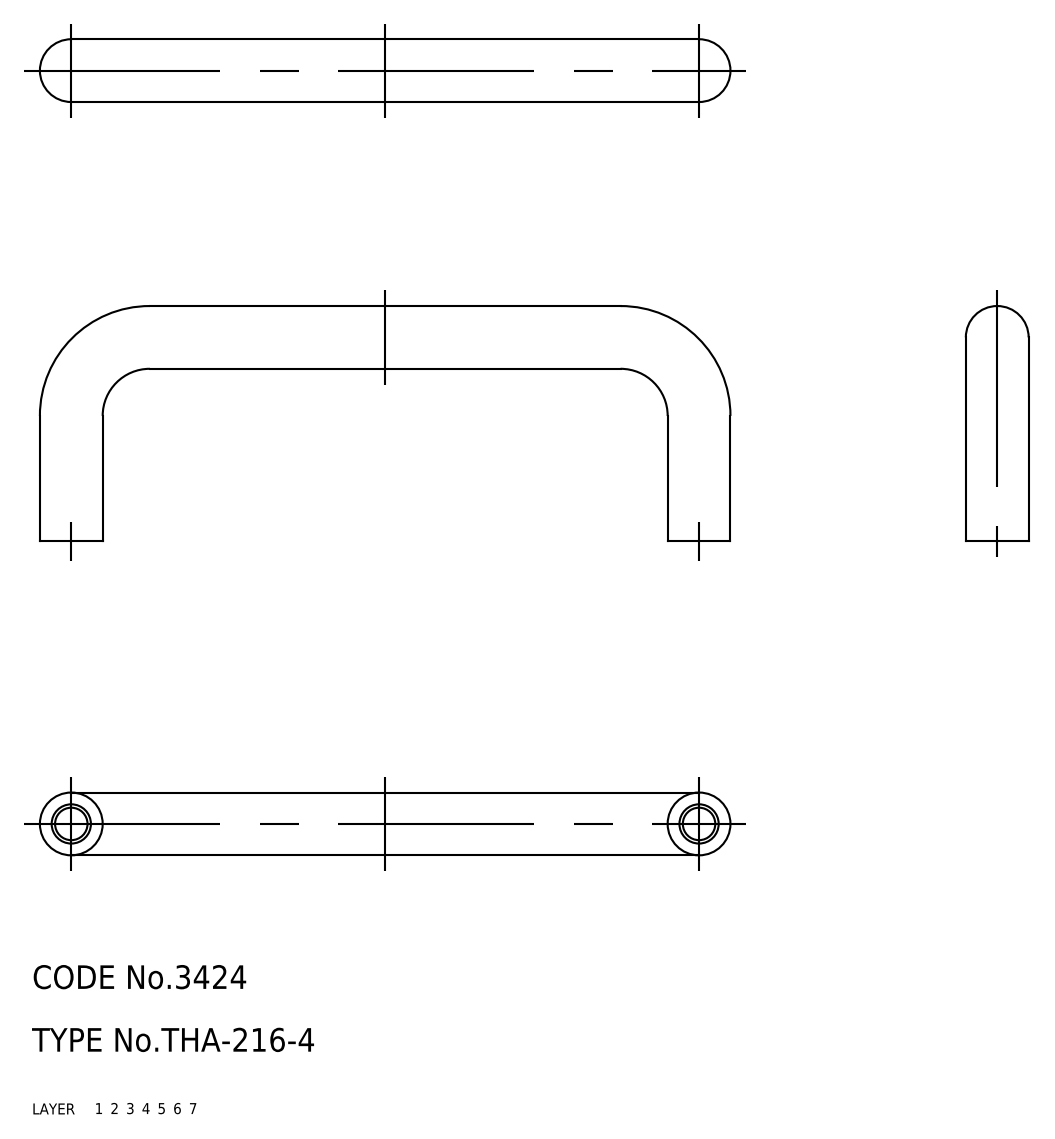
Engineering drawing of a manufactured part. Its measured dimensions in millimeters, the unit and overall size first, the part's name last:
Units: millimetres
Overall size (bounding box): 88 × 30 × 8
Volume: 5 733 mm³ · Surface area: 3 581 mm²
Bodies: 1 solid, 18 faces (0 planar, 0 cylindrical, 18 other)
Part name (STEP PRODUCT): pull
STEP written by: CADfix (AUTOMOTIVE_DESIGN)
